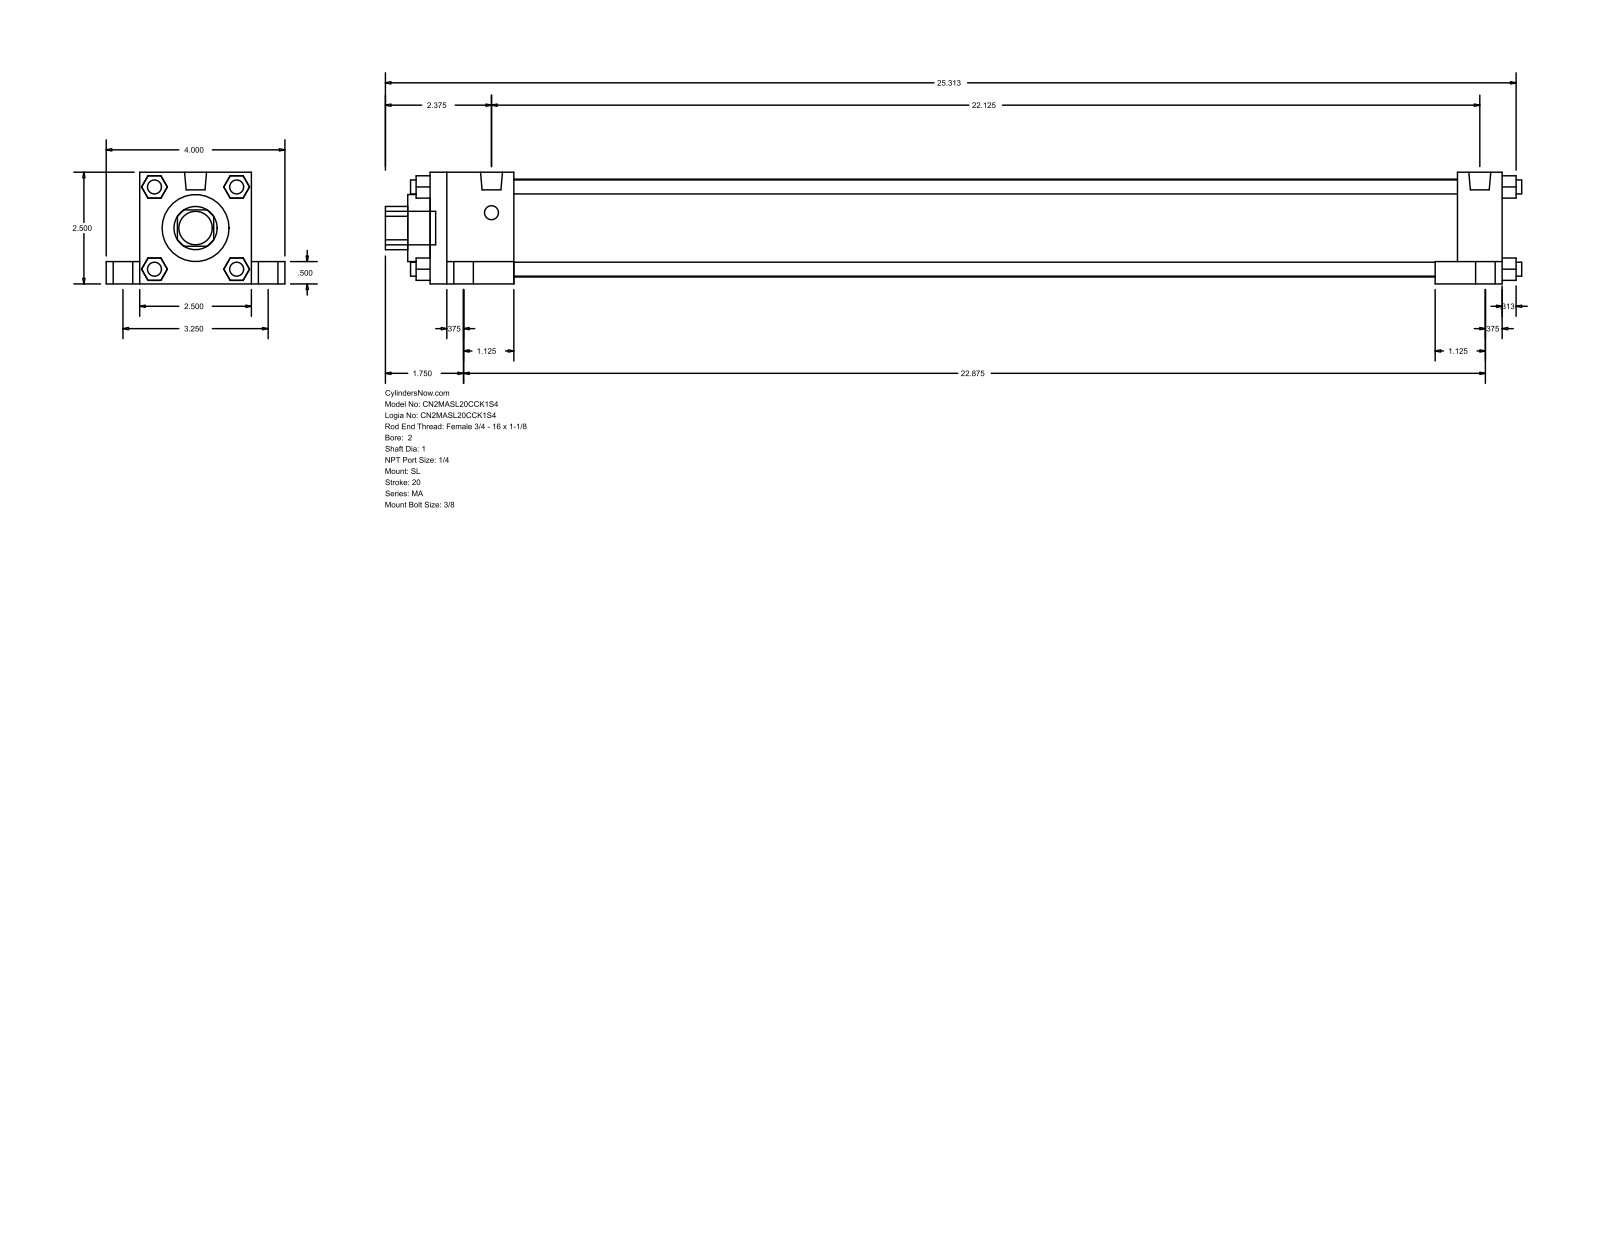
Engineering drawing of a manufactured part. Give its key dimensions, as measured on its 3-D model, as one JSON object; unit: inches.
{"part_name": "MA_SL__0200_1", "step_written_by": "GSSL Pune (CONFIG_CONTROL_DESIGN)", "units": "inches", "bodies": {"solids": 0, "faces": 148, "planar": 112, "cylindrical": 36, "other": 0}, "overall_size": [25.437, 4, 2.5], "round_holes": [[1, 1], [1.5, 1], [2.19, 1]], "round_bosses_or_shafts": [[0.313, 8], [0.687, 4], [0.437, 4], [0.492, 2], [0.75, 1]], "partial_cylinders_radius": [[0.484, 1]], "face_to_face_distances": [2.5, 0.5, 24, 0.75, 3.25, 1, 2, 1.875, 22.125, 23]}
